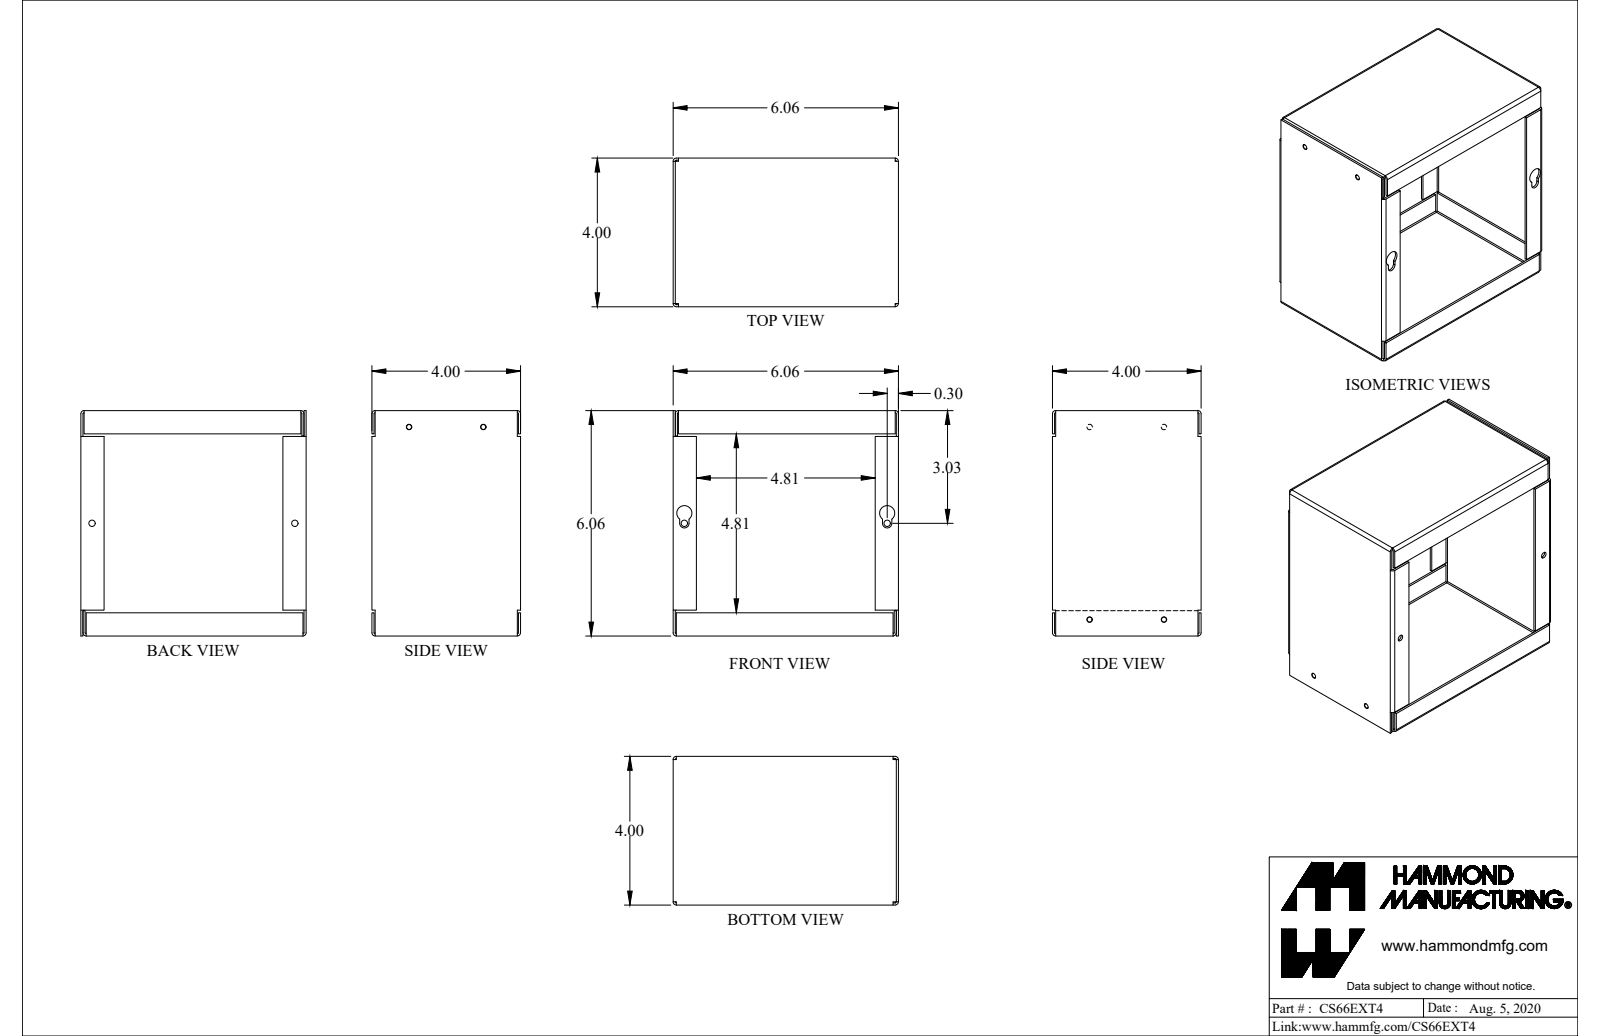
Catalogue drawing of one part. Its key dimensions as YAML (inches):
part_name: "CS66EXT4"
step_written_by: "SolidWorks 2021 (AUTOMOTIVE_DESIGN)"
units: inches
bodies: {solids: 2, faces: 114, planar: 76, cylindrical: 38, other: 0}
overall_size: [6.063, 6.063, 4]
volume: 6.976
surface_area: 249.4
round_holes:
  - {diameter: 0.145, count: 4}
  - {diameter: 0.17, count: 2}
round_bosses_or_shafts:
  - {diameter: 0.131, count: 4}
partial_cylinders:
  - {radius: 0.029, count: 12}
  - {radius: 0.086, count: 12}
  - {radius: 0.125, count: 2}
  - {radius: 0.203, count: 2}
face_to_face_distances: [6.006, 0.057, 0.057, 5.948, 6.063, 6.062, 5.949, 3.943, 4, 3.886]
hole_center_spacings: [2, 5.18, 5.553, 5.459]
